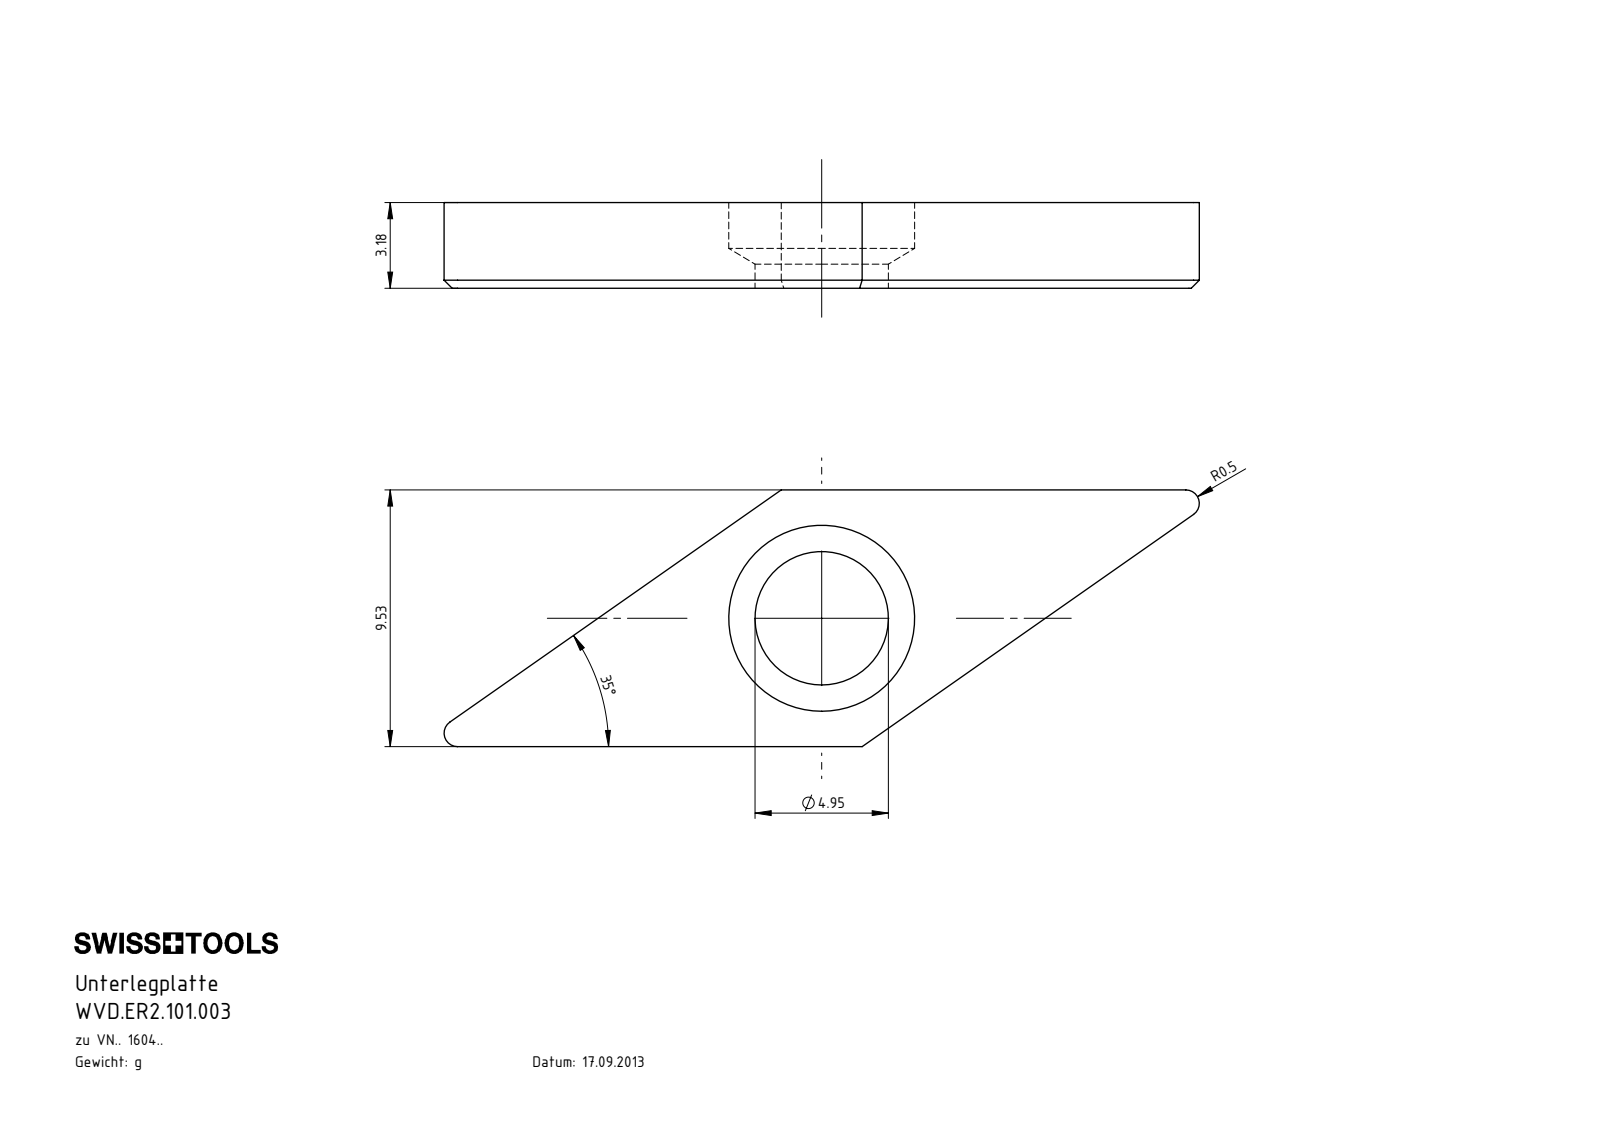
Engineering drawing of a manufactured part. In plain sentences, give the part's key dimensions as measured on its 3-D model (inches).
The part is named "WVD.ER2.101.003". Its 3-D file was written by "SolidWorks 2017 (AUTOMOTIVE_DESIGN)". It is 1 solid with 17 faces: 10 planar, 4 cylindrical and 3 other. Overall it measures 1.104 by 0.375 by 0.125 inches. Its volume is 0.024 cubic inches and its surface area 0.803 square inches. Round holes: 1 of diameter 0.195, 1 of diameter 0.272. Partial cylindrical surfaces (rounded edges, fillets, slot ends): 2 of radius 0.02. The main face-to-face distances are 0.125, 0.375, 0.375.
